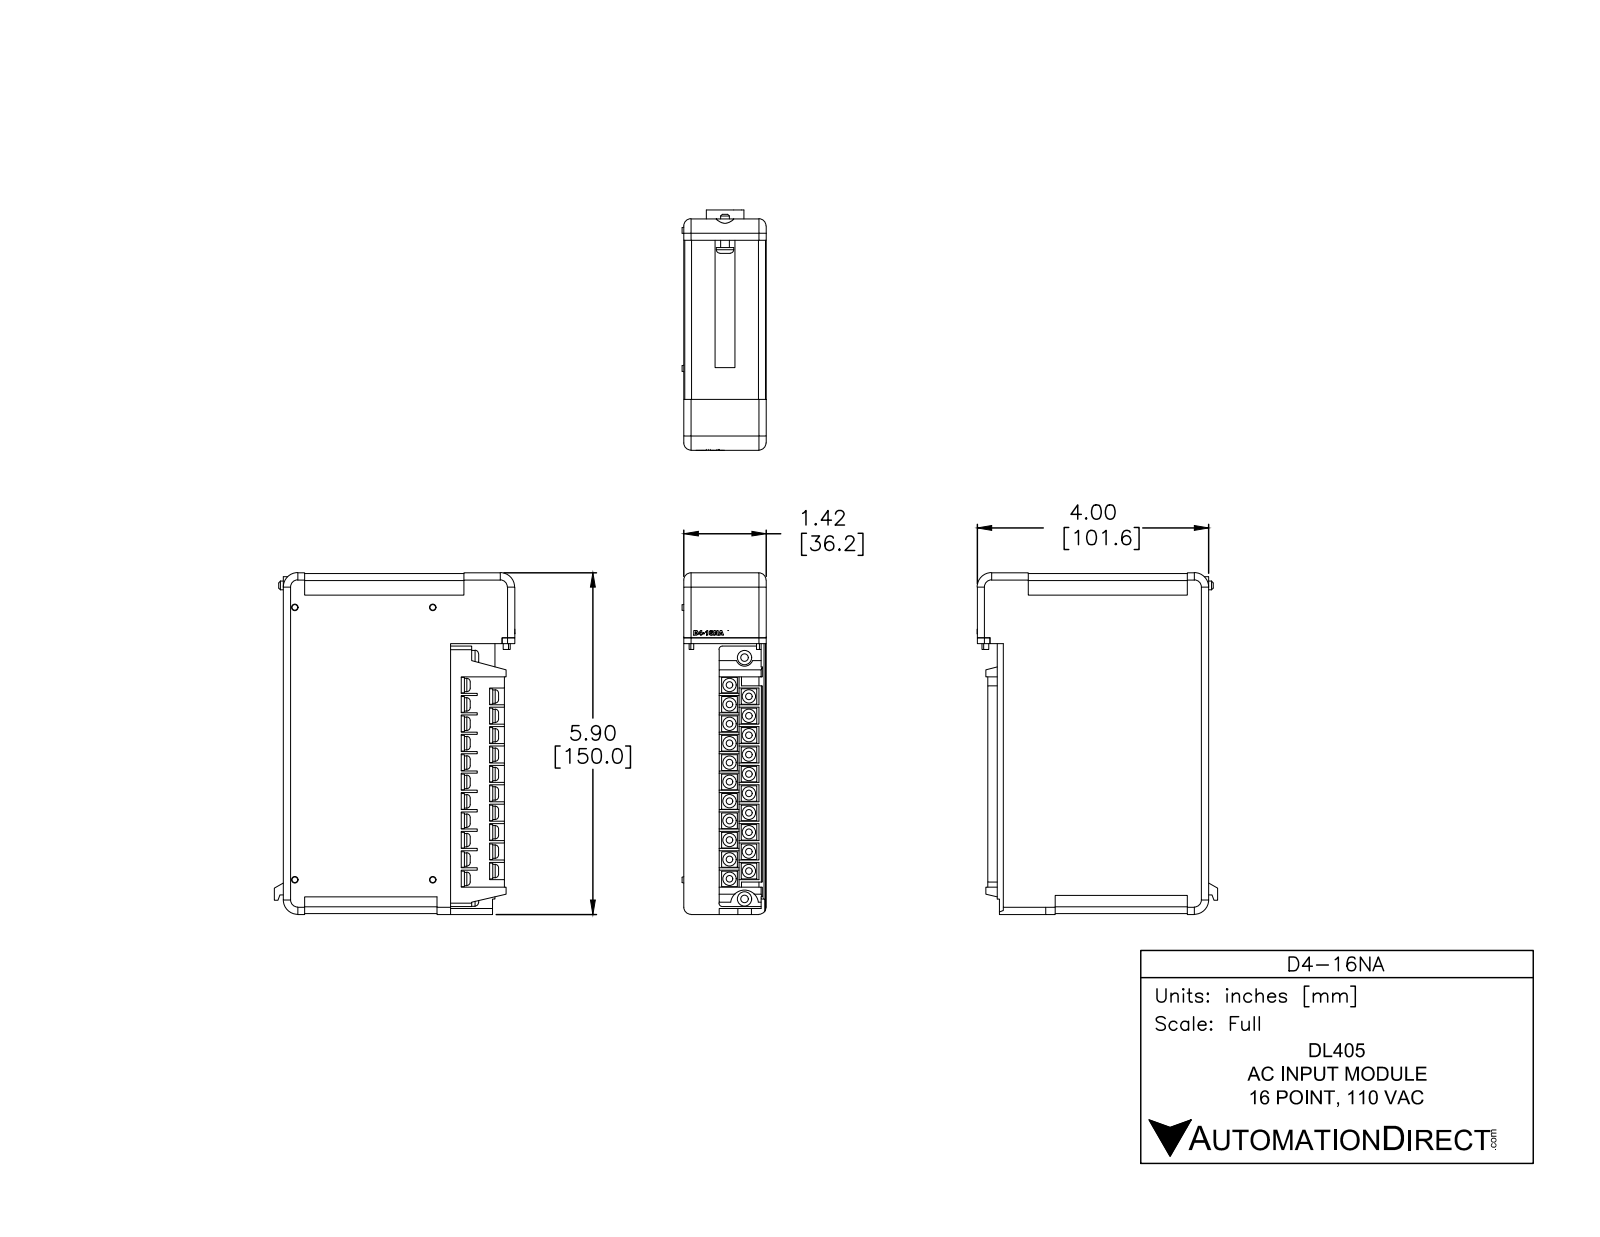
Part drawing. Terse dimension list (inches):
name: D4-16NA
written by: SolidWorks 2014 (AUTOMOTIVE_DESIGN)
unit: in
bodies: 13 solids, 585 faces (412 planar, 86 cylindrical, 87 other)
size: 5.905 × 4.156 × 1.455
volume: 27.51 in³; area: 86.82 in²
bosses: 21× ⌀0.23, 2× ⌀0.25, 1× ⌀0.3, 1× ⌀0.15
rounds: 8× R0.125, 4× R0.12, 3× R0.25, 2× R0.015, 2× R0.03, 2× R0.06, 1× R0.149, 1× R0.151
face distances: 1.425, 0.015, 2.89, 5.875, 1.41, 0.47, 0.2, 0.955, 5.89, 1.21
